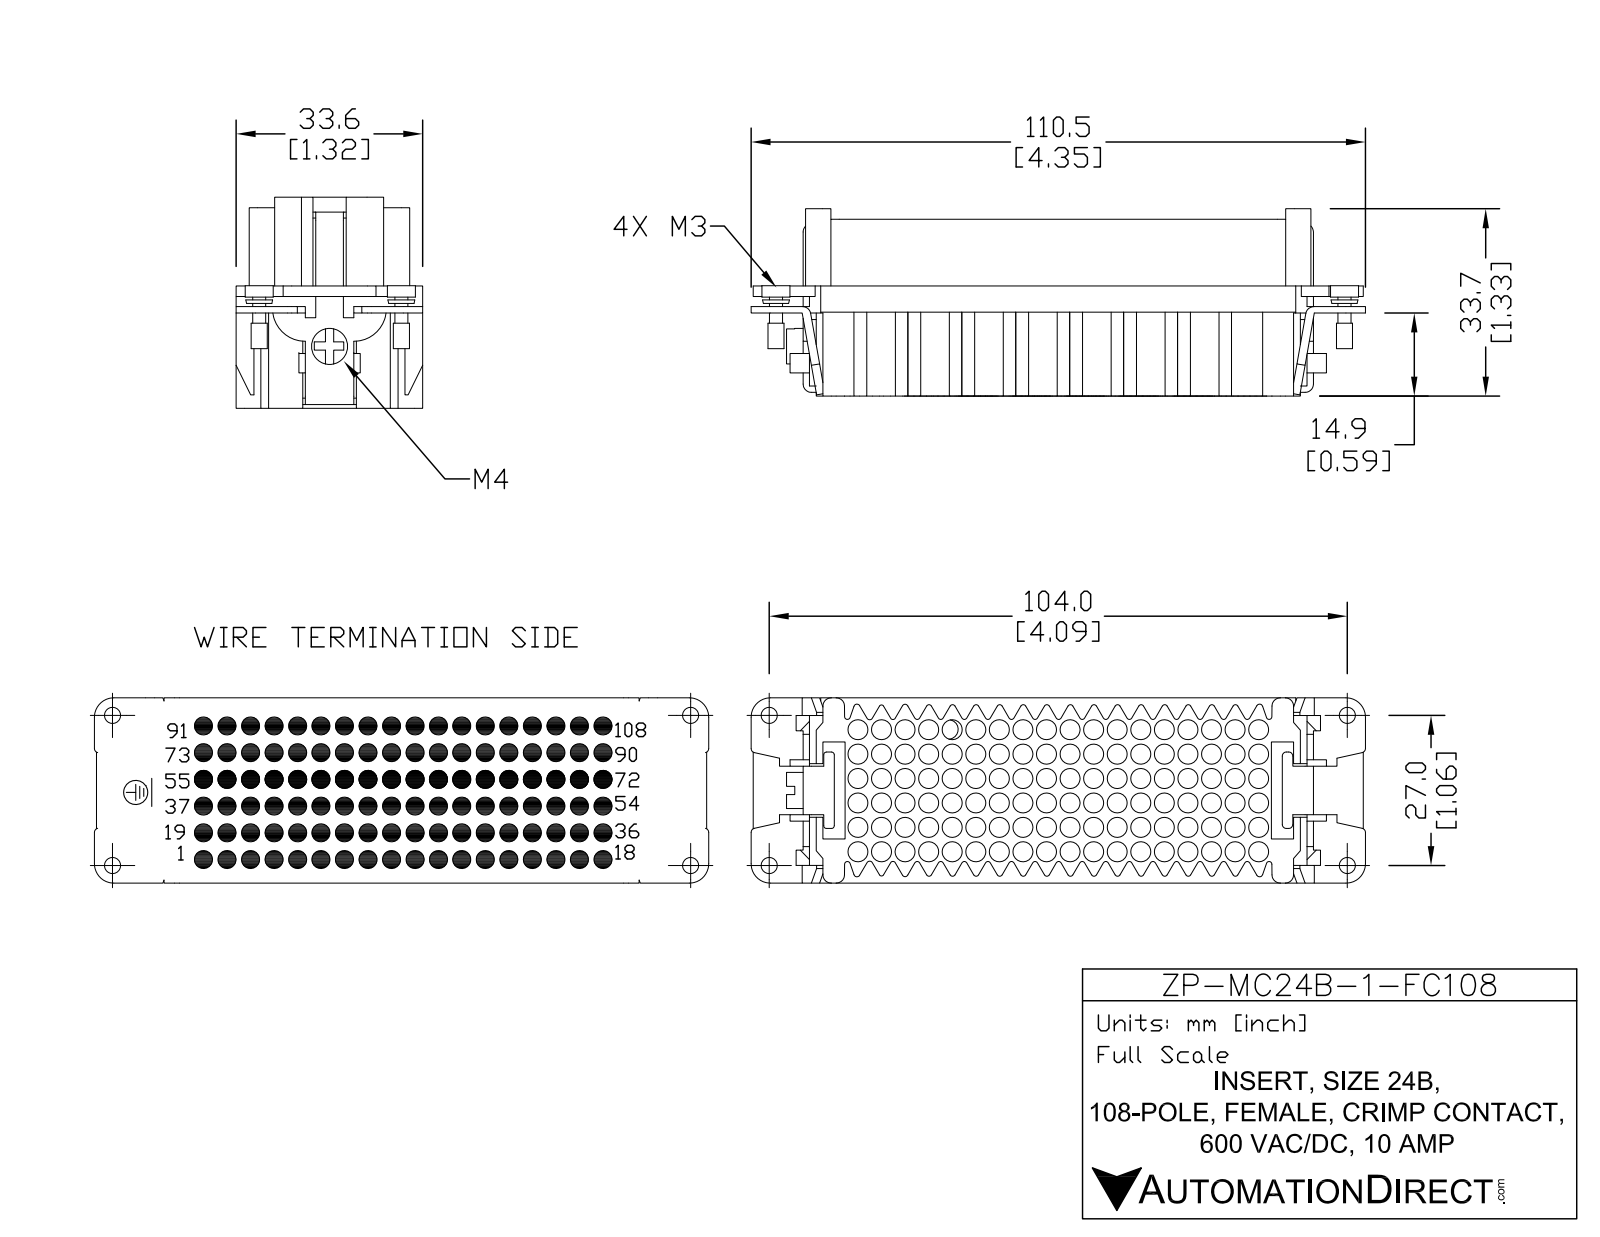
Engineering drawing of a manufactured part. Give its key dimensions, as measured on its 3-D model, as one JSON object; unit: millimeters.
{"part_name": "ZP-24B-108-FC-INSERT", "step_written_by": "SolidWorks 2011 (AUTOMOTIVE_DESIGN)", "units": "millimeters", "bodies": {"solids": 2, "faces": 955, "planar": 589, "cylindrical": 362, "other": 4}, "overall_size": [110.75, 38.05, 33.4], "volume_mm3": 52490, "surface_area_mm2": 65005, "round_holes": [[3.5, 108], [3.6, 108], [3, 1]], "round_bosses_or_shafts": [[5.05, 4], [2.9, 4], [2.35, 4], [6.5, 1]], "partial_cylinders_radius": [[0.5, 40], [0.5, 28], [1.5, 18], [0.75, 8], [0.57, 4], [1.54, 4], [3.5, 4], [0.41, 2]], "face_to_face_distances": [14.1, 22.05, 36.15, 3.67, 28.7, 1.15, 2.35, 31.05, 1.21, 14.69], "hole_center_spacings": [4.25, 8.5, 12.75, 6.12, 9.57, 17, 13.49, 17.56]}
